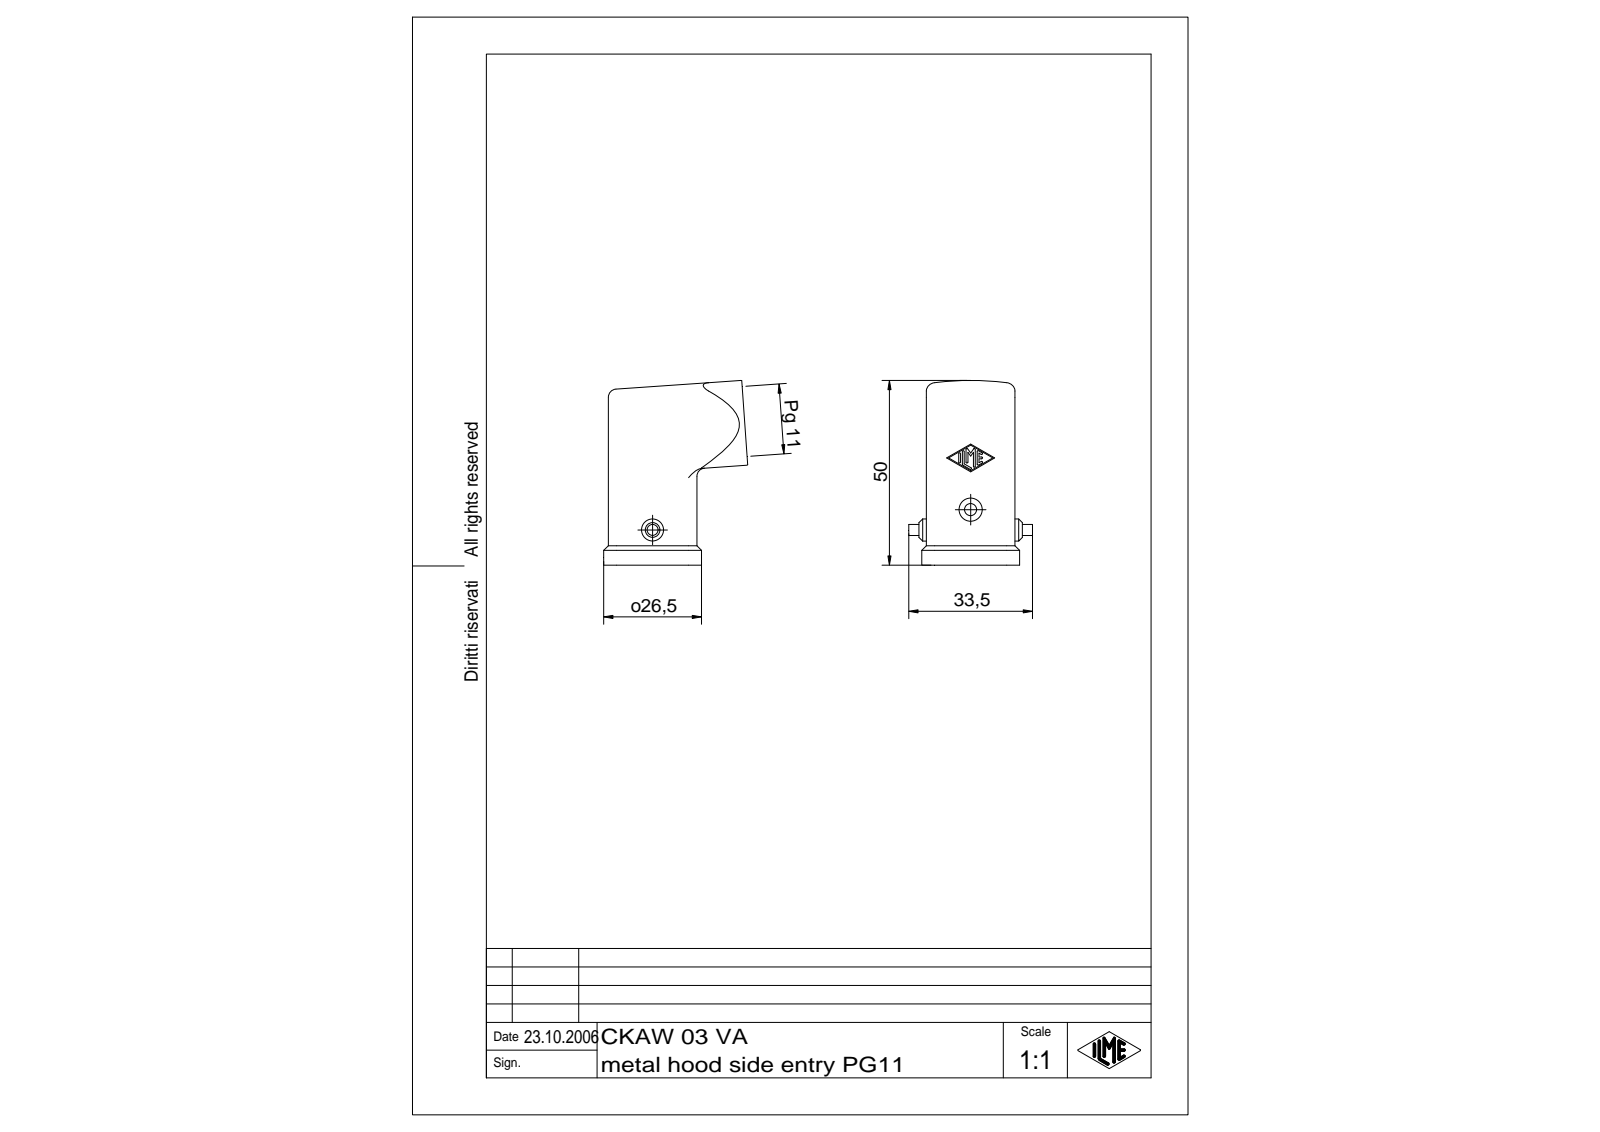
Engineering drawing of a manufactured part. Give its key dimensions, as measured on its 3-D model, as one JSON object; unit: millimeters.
{"step_written_by": "Autodesk Inventor 7 (AUTOMOTIVE_DESIGN)", "units": "millimeters", "bodies": {"solids": 1, "faces": 146, "planar": 71, "cylindrical": 52, "other": 23}, "overall_size": [49.98, 38.98, 33.5], "volume_mm3": 9603, "surface_area_mm2": 11325, "round_holes": [[3.3, 1], [14.5, 1], [17.26, 1]], "round_bosses_or_shafts": [[6, 1], [3, 1]], "partial_cylinders_radius": [[0.25, 14], [2.25, 8], [1.25, 4], [3.5, 4]], "face_to_face_distances": [23, 1, 24, 22, 1.25, 2.25, 24.25, 25.25, 3, 2]}
